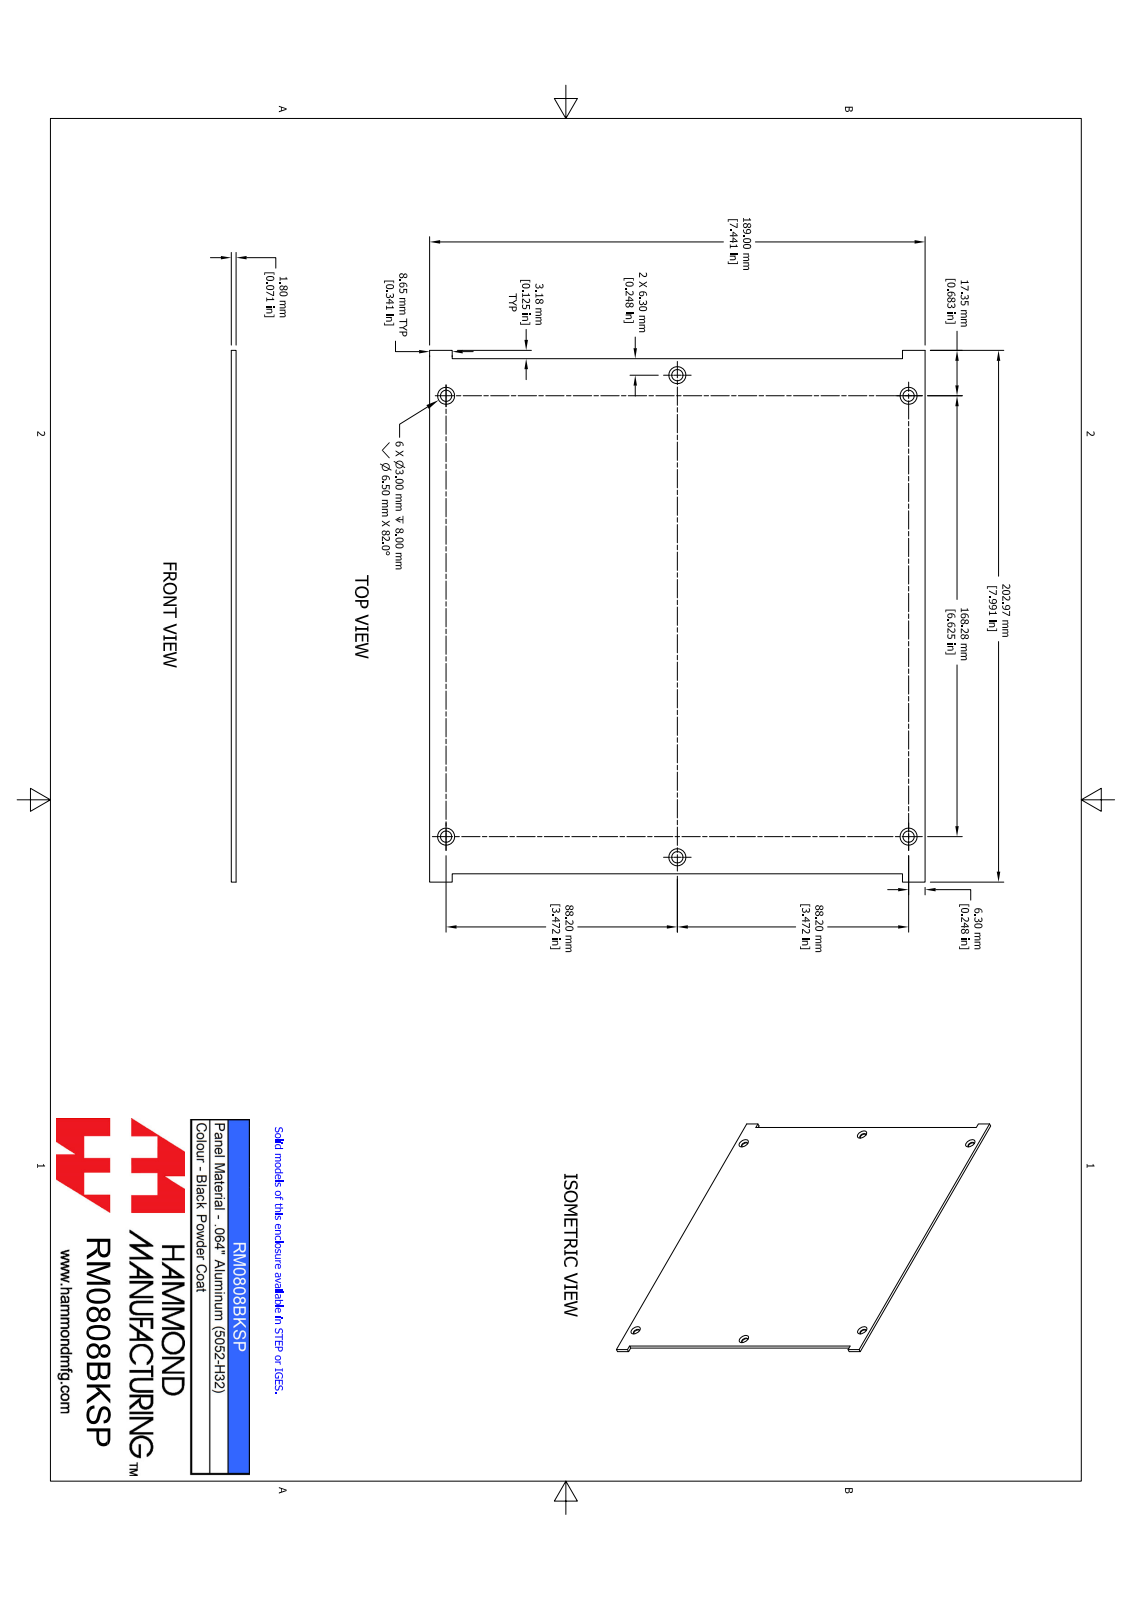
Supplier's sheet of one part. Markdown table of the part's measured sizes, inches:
| quantity | value |
| --- | --- |
| part name | RM0808BKSP |
| STEP written by | SolidWorks 2021 (AUTOMOTIVE_DESIGN) |
| units | inches |
| bodies | 1 solid, 26 faces (14 planar, 6 cylindrical, 6 other) |
| overall size | 7.991 × 7.441 × 0.071 |
| volume | 4.08 in³ |
| surface area | 117.7 in² |
| round holes (diameter × count) | 0.169 × 6 |
| main face-to-face distances | 0.071, 7.441, 7.741, 7.866, 0.125, 0.125, 7.866, 7.991, 0.341, 7.1 |
| hole center spacings | 3.486, 6.625, 6.945, 7.756, 7.756, 9.598, 7.245 |
